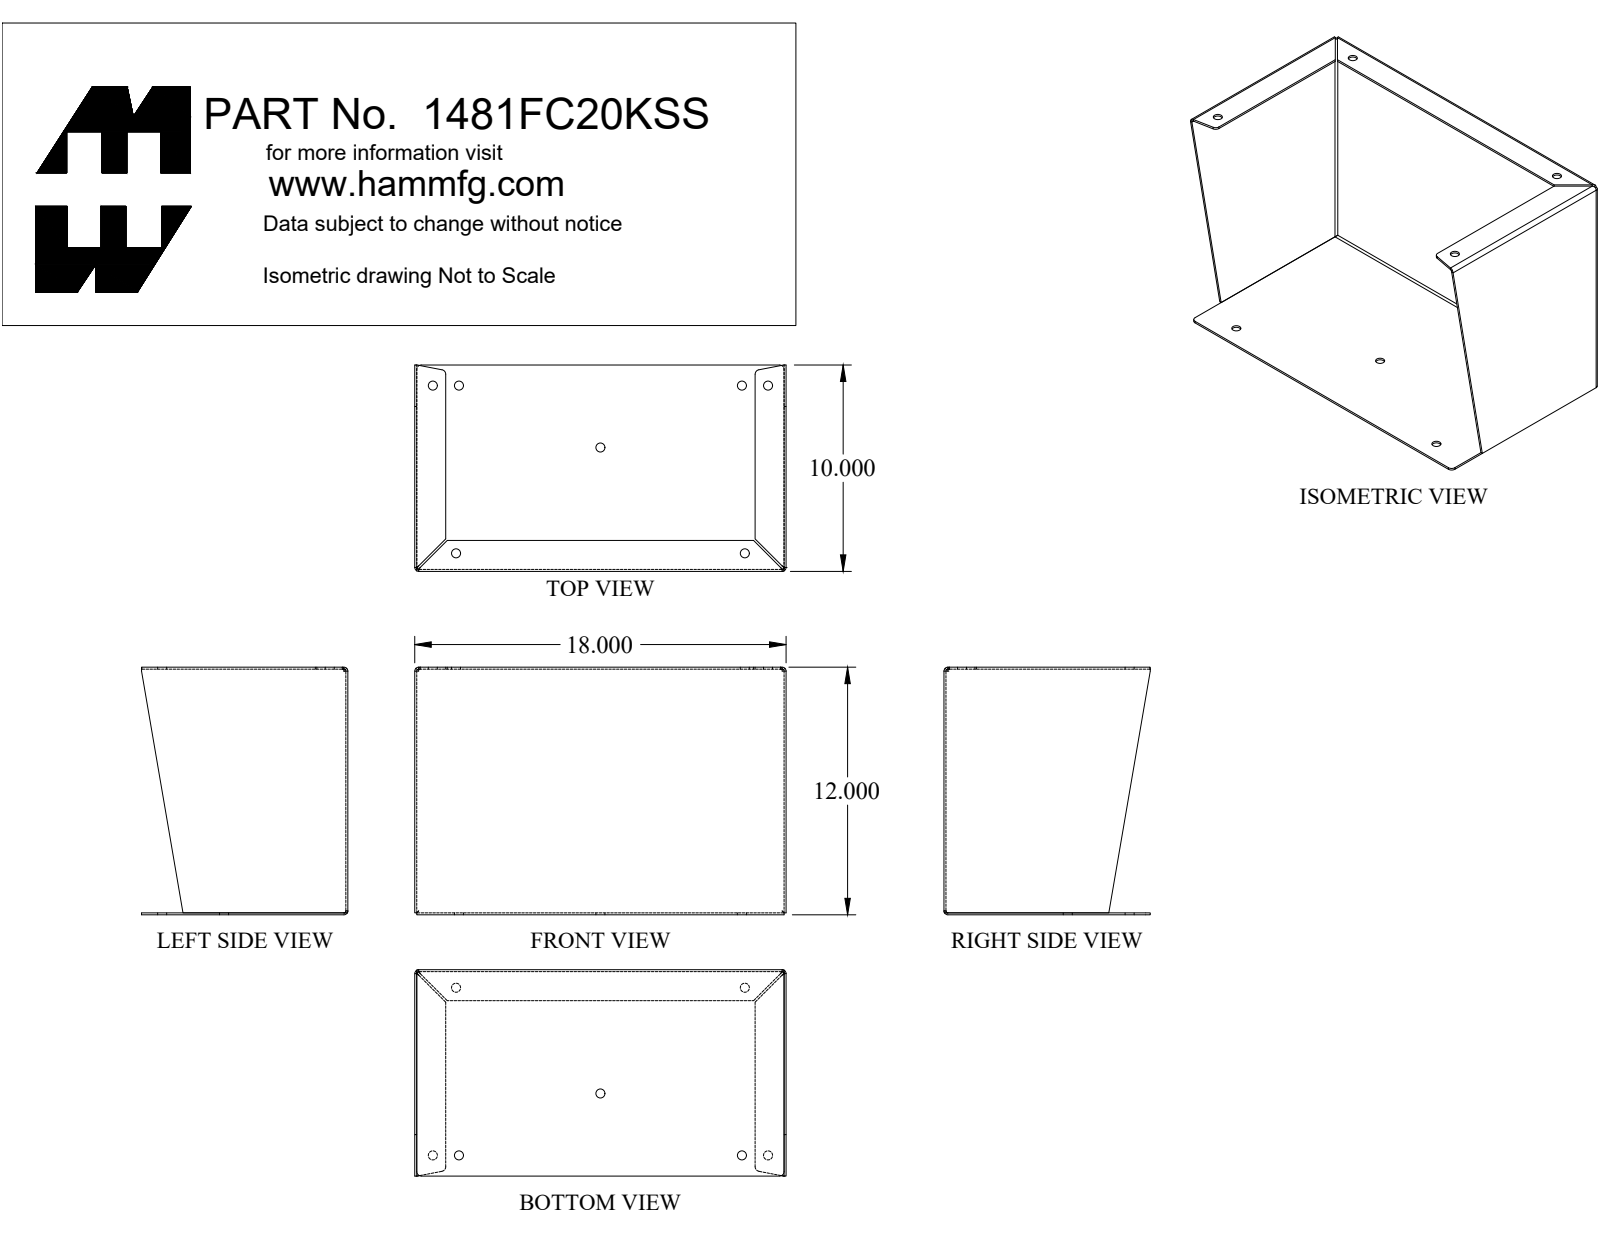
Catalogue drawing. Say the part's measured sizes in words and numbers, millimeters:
The part is named "1481FC20KSS". Its 3-D file was written by "SolidWorks 2019 (CONFIG_CONTROL_DESIGN)". It is 1 solid with 71 faces: 42 planar, 23 cylindrical and 6 other. Overall it measures 508 by 304.8 by 254 millimeters. Its volume is 1 079 000 cubic millimeters and its surface area 902 600 square millimeters. Round holes: 7 of diameter 11.1. Partial cylindrical surfaces (rounded edges, fillets, slot ends): 6 of radius 2.4, 6 of radius 4.8, 4 of radius 5.6. The main face-to-face distances are 2.4, 505.6, 2.4, 508, 503.2, 300, 302.4, 302.4, 304.8, 35.7. The hole center spacings are 32.2, 206.4, 208.3, 213.7, 241.3, 244, 431.4, 452.6.
